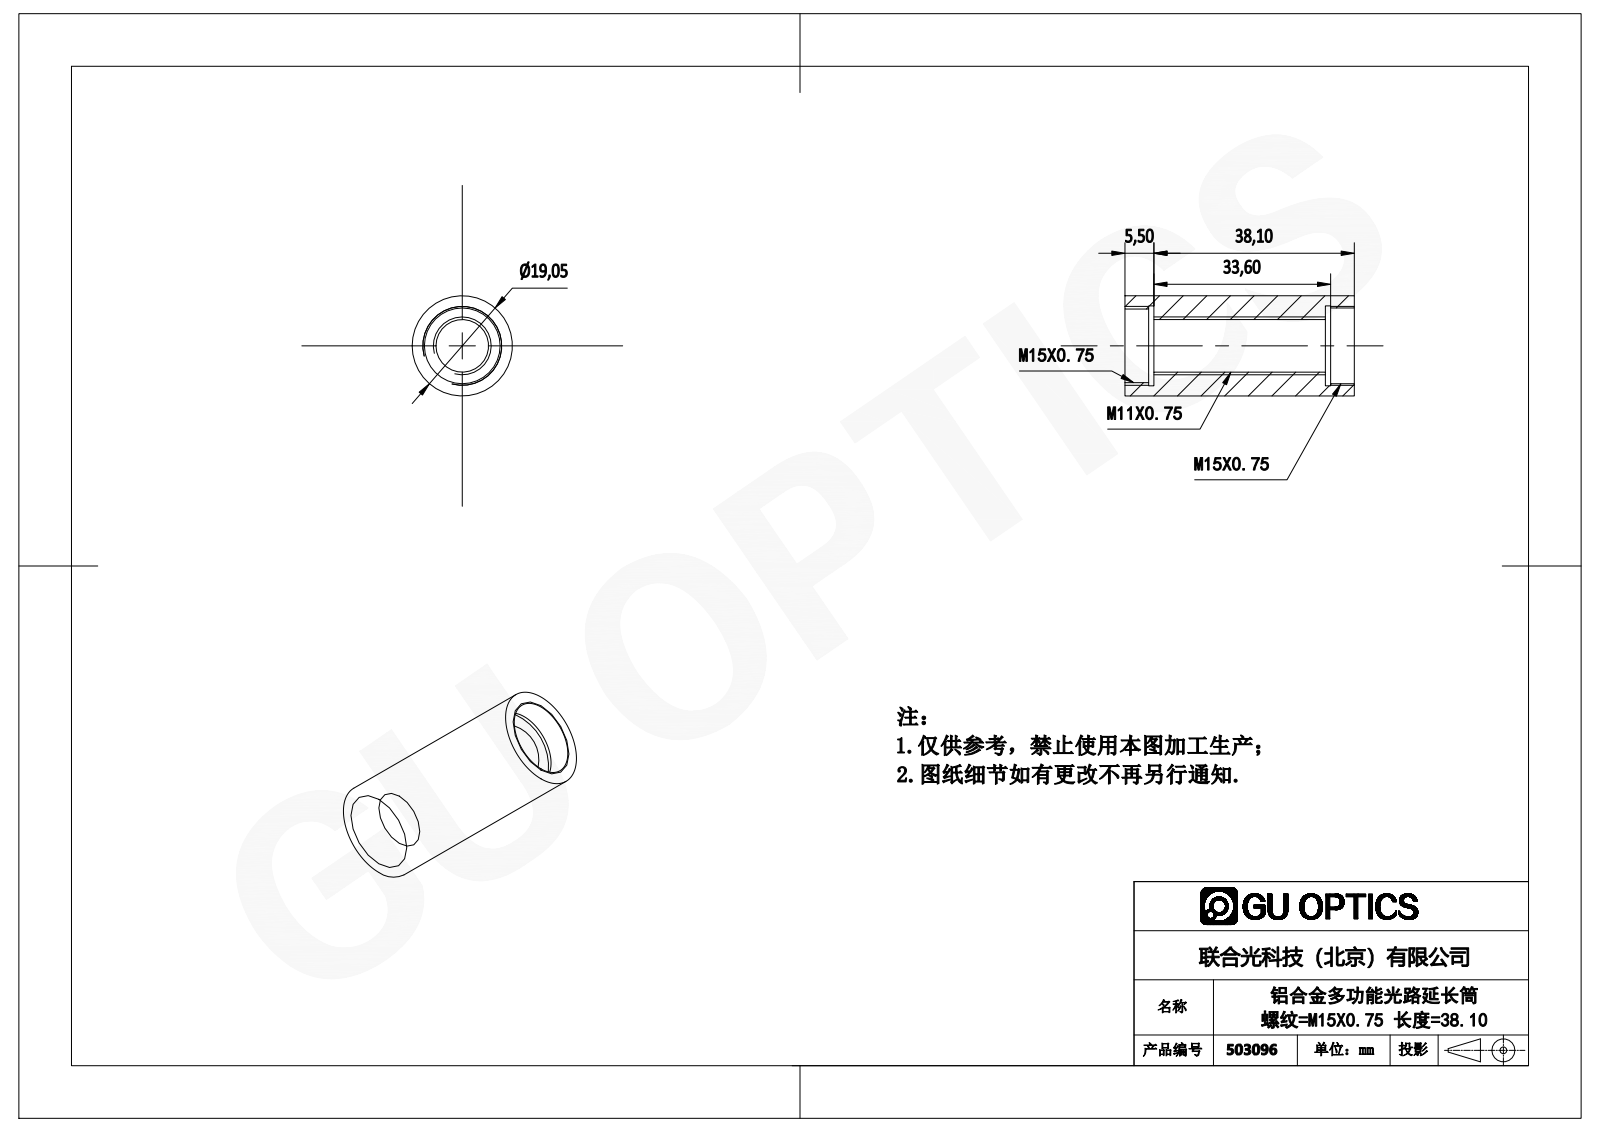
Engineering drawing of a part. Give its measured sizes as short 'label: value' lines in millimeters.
name: 503096
written by: SolidWorks 2016 (AUTOMOTIVE_DESIGN)
unit: mm
bodies: 1 solid, 18 faces (6 planar, 12 cylindrical, 0 other)
size: 43.6 × 19.05 × 19.05
volume: 8 078 mm³; area: 4 636 mm²
holes: 1× ⌀10, 1× ⌀14, 1× ⌀14.4, 1× ⌀15.2
bosses: 1× ⌀19.05
face distances: 5.5, 38.1, 43.6, 32.6, 4.5, 39.1, 1, 33.6, 34.6
